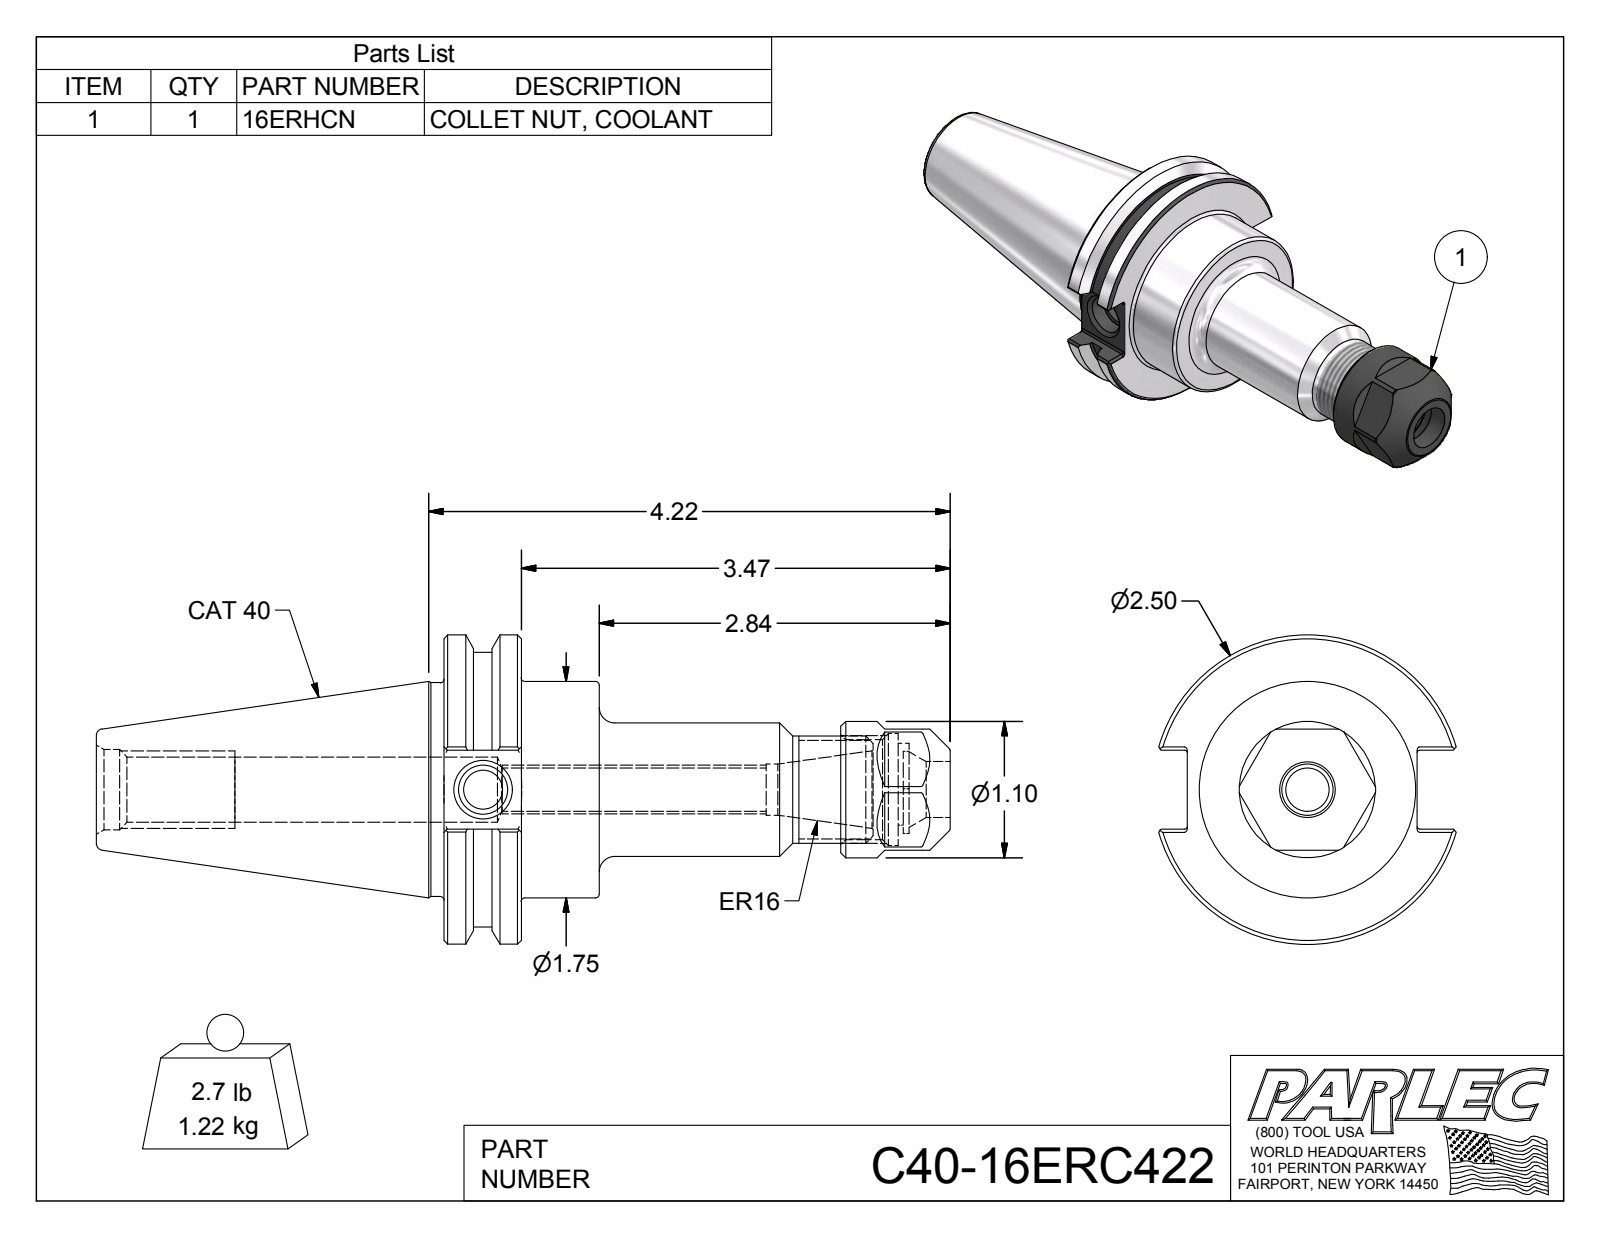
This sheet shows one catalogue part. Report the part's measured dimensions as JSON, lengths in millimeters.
{"part_name": "C40-16ER4-1; 16ERHCN; C40-16ERC422", "step_written_by": "Autodesk Inventor 2016 (AUTOMOTIVE_DESIGN)", "units": "millimeters", "bodies": {"solids": 2, "faces": 122, "planar": 50, "cylindrical": 35, "other": 37}, "overall_size": [175.45, 63.5, 61.05], "volume_mm3": 155149, "surface_area_mm2": 32752, "round_holes": [[8, 1], [8.92, 1], [10.13, 1], [10.5, 1], [11.5, 1], [13.38, 1], [13.39, 1], [16.46, 1], [16.8, 1], [20.5, 1], [23, 1]], "round_bosses_or_shafts": [[63.5, 1], [56.36, 1], [44.45, 1], [43.94, 1], [28, 1], [27.43, 1], [22, 1]], "partial_cylinders_radius": [[0.51, 12], [9, 1]], "face_to_face_distances": [15.88, 31.88, 16, 24.86, 4.3, 20.56, 93.32, 77.44, 61.44, 16.26], "hole_center_spacings": [1.3]}
